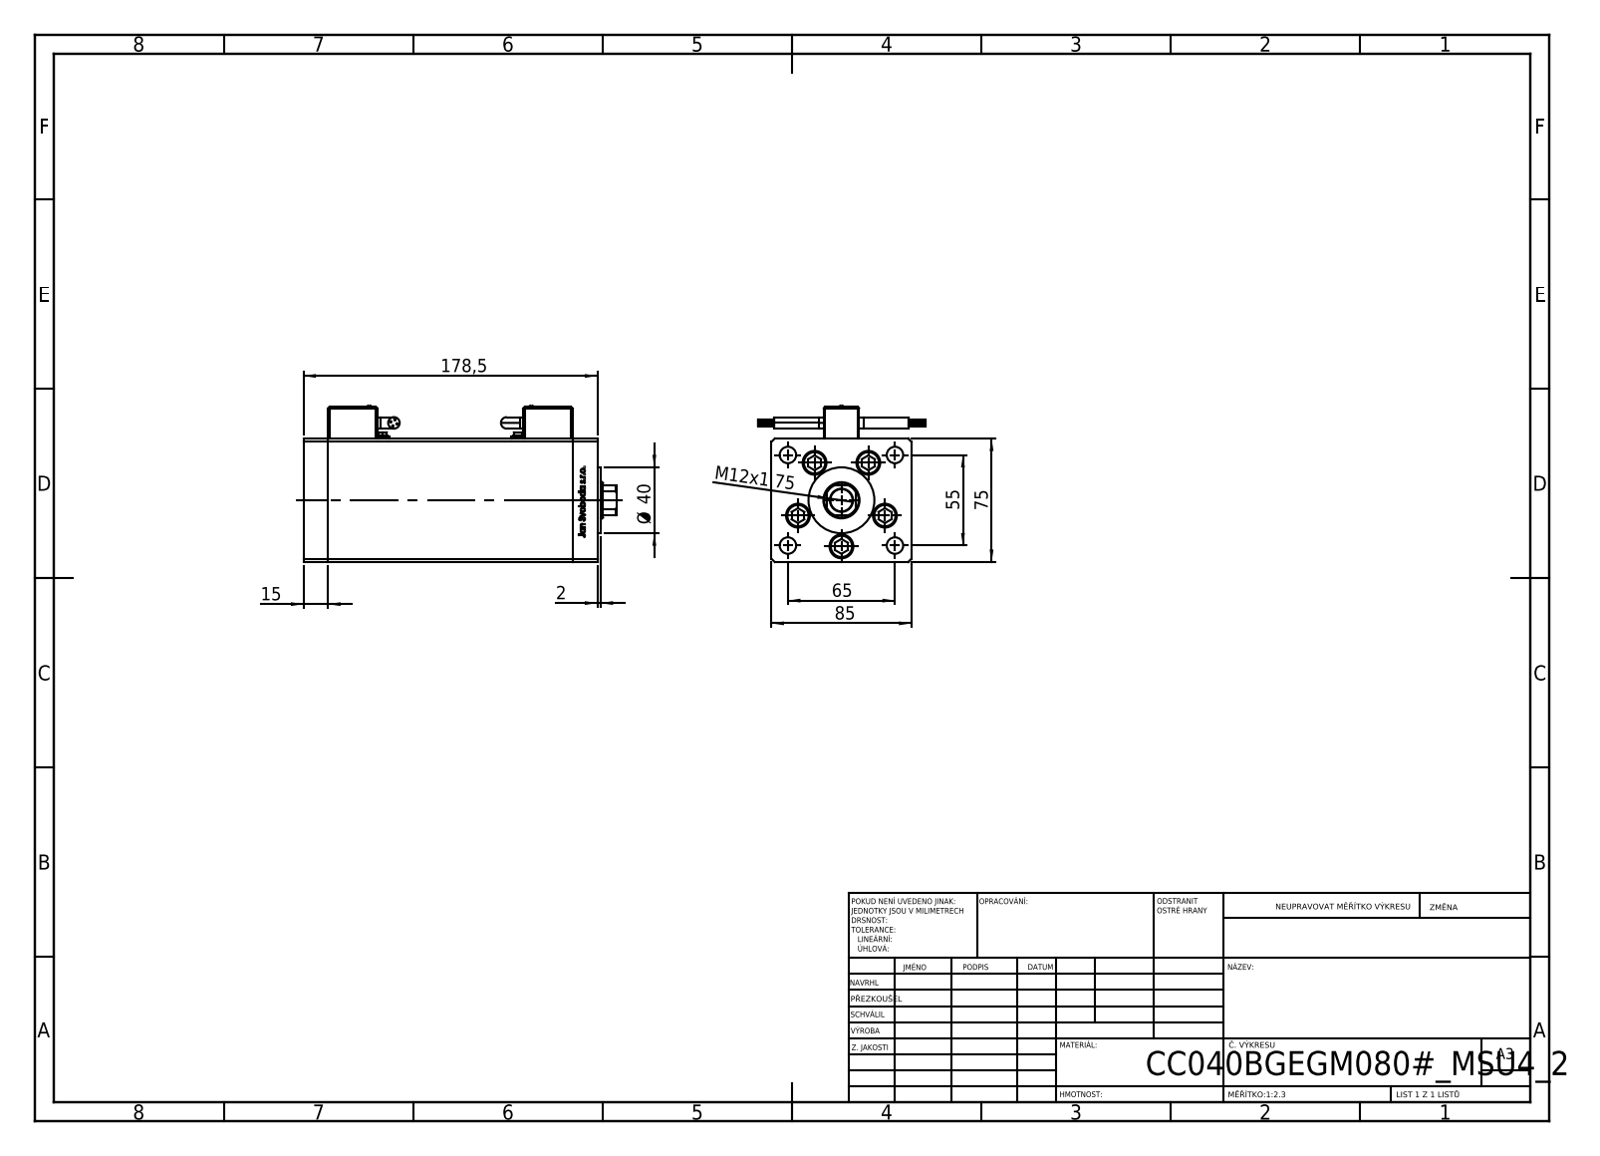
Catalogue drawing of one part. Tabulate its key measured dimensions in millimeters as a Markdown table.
| quantity | value |
| --- | --- |
| part name | ALLEN BOLT; Magnetic_Switch_MSU4; V220C BACK_B; V220C_B MIDDLE (+2 more) |
| STEP written by | SolidWorks 2019 (CONFIG_CONTROL_DESIGN) |
| units | millimeters |
| bodies | 16 solids, 1389 faces (542 planar, 237 cylindrical, 610 other) |
| overall size | 190 × 101.6 × 95.1 |
| volume | 1 049 000 mm³ |
| surface area | 171 822 mm² |
| round holes (diameter × count) | 11 × 5, 14.5 × 5, 10 × 4, 2 × 2, 3.6 × 2, 5 × 2, 7 × 2, 13.16 × 2, 13.5 × 1, 22 × 1 |
| round bosses / shafts (diameter × count) | 0.85 × 8, 8 × 5, 7 × 4, 6 × 2, 3.5 × 2, 2.5 × 2, 40 × 1 |
| partial cylindrical surfaces (radius × count) | 1 × 24, 4 × 4, 0.93 × 2, 10.5 × 1 |
| main face-to-face distances | 85, 75, 15, 148.5, 163.5, 178.5, 68.5, 34.25, 6.5, 31.7 |
| hole center spacings | 28, 42.57, 8.25, 16.86, 19.17, 32.33, 32.5, 33.63 |
